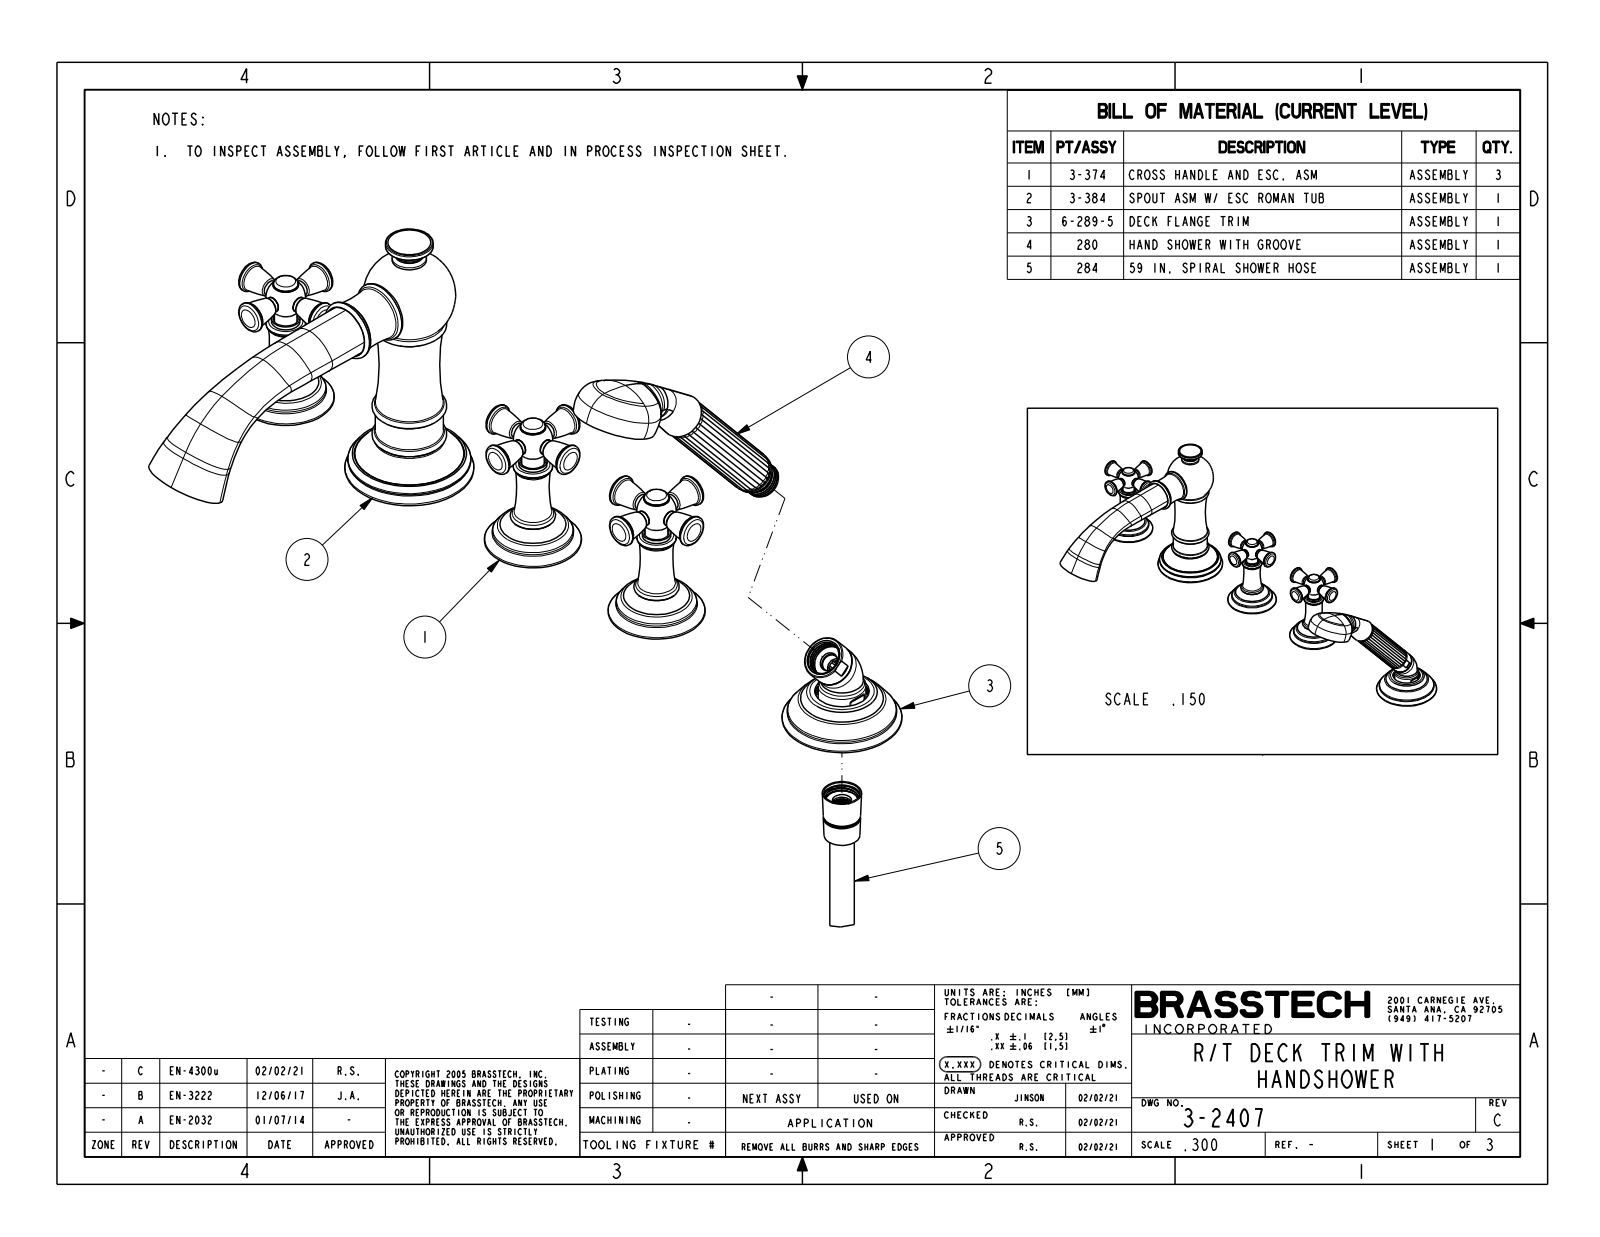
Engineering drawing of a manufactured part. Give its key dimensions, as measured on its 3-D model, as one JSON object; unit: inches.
{"part_name": "3-2407", "step_written_by": "CREO PARAMETRIC BY PTC INC, 2018400 (CONFIG_CONTROL_DESIGN)", "units": "inches", "bodies": {"solids": 5, "faces": 926, "planar": 87, "cylindrical": 206, "other": 633}, "overall_size": [20.64, 9.187, 6.585], "volume_in3": 44.29, "surface_area_in2": 187.9, "round_holes": [[0.046, 52]], "round_bosses_or_shafts": [[0.72, 4], [0.36, 4], [0.9, 3], [0.649, 3], [0.56, 3], [0.517, 3], [1.823, 1], [1.65, 1]], "partial_cylinders_radius": [[0.05, 6]], "face_to_face_distances": [0.775, 2.14, 1.365, 2.22, 1.445, 0.08, 3.171, 2.396, 1.031, 0.951], "hole_center_spacings": [0.367, 0.497, 0.185, 0.185, 0.187, 0.355, 0.184, 0.659]}
